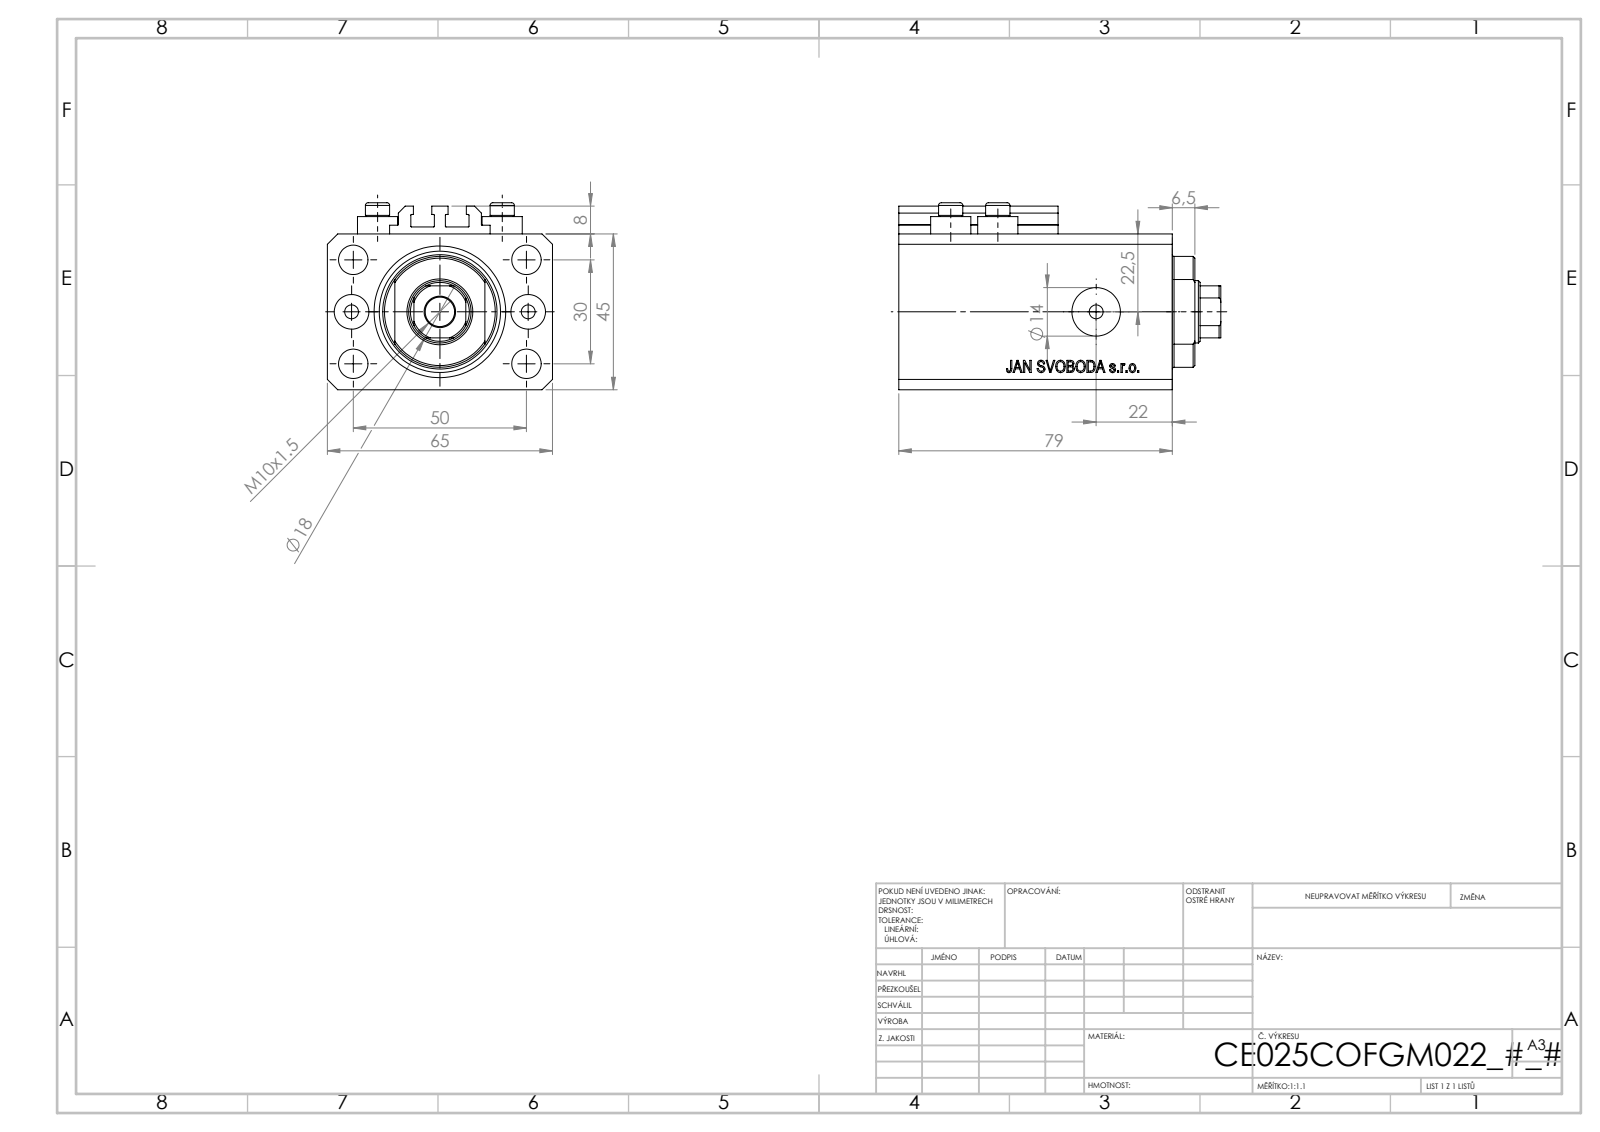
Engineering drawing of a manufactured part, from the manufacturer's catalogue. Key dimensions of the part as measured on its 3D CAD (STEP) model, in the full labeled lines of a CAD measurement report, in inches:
Part name (STEP PRODUCT): V250CE_VC_C; V250CE_C_VCP; V250CE_C_Body; ALLEN BOLT V250CE
STEP written by: SolidWorks 2019 (CONFIG_CONTROL_DESIGN)
Units: inches
Bodies: 8 solids, 1034 faces (504 planar, 86 cylindrical, 444 other)
Overall size (bounding box): 3.661 × 2.559 × 2.126
Volume: 13.25 in³ · Surface area: 90.48 in²
Round holes (diameter × count): ⌀0.157 ×8, ⌀0.335 ×5, ⌀0.394 ×2, ⌀0.551 ×2, ⌀0.709 ×1, ⌀0.984 ×1, ⌀1.496 ×1
Round bosses / shafts (diameter × count): ⌀0.457 ×4, ⌀0.276 ×4
Partial cylindrical surfaces — rounded edges, fillets, slot ends (radius × count): R0.008 ×10, R0.335 ×1, R0.63 ×1
Main face-to-face distances: 1.772, 2.559, 0.551, 3.11, 0.118, 0.272, 2.287, 2.839, 1.85, 0.807
Hole centre spacings: 0.591, 1.148, 2.074, 0.535, 1.004, 1.181, 1.417, 1.515
